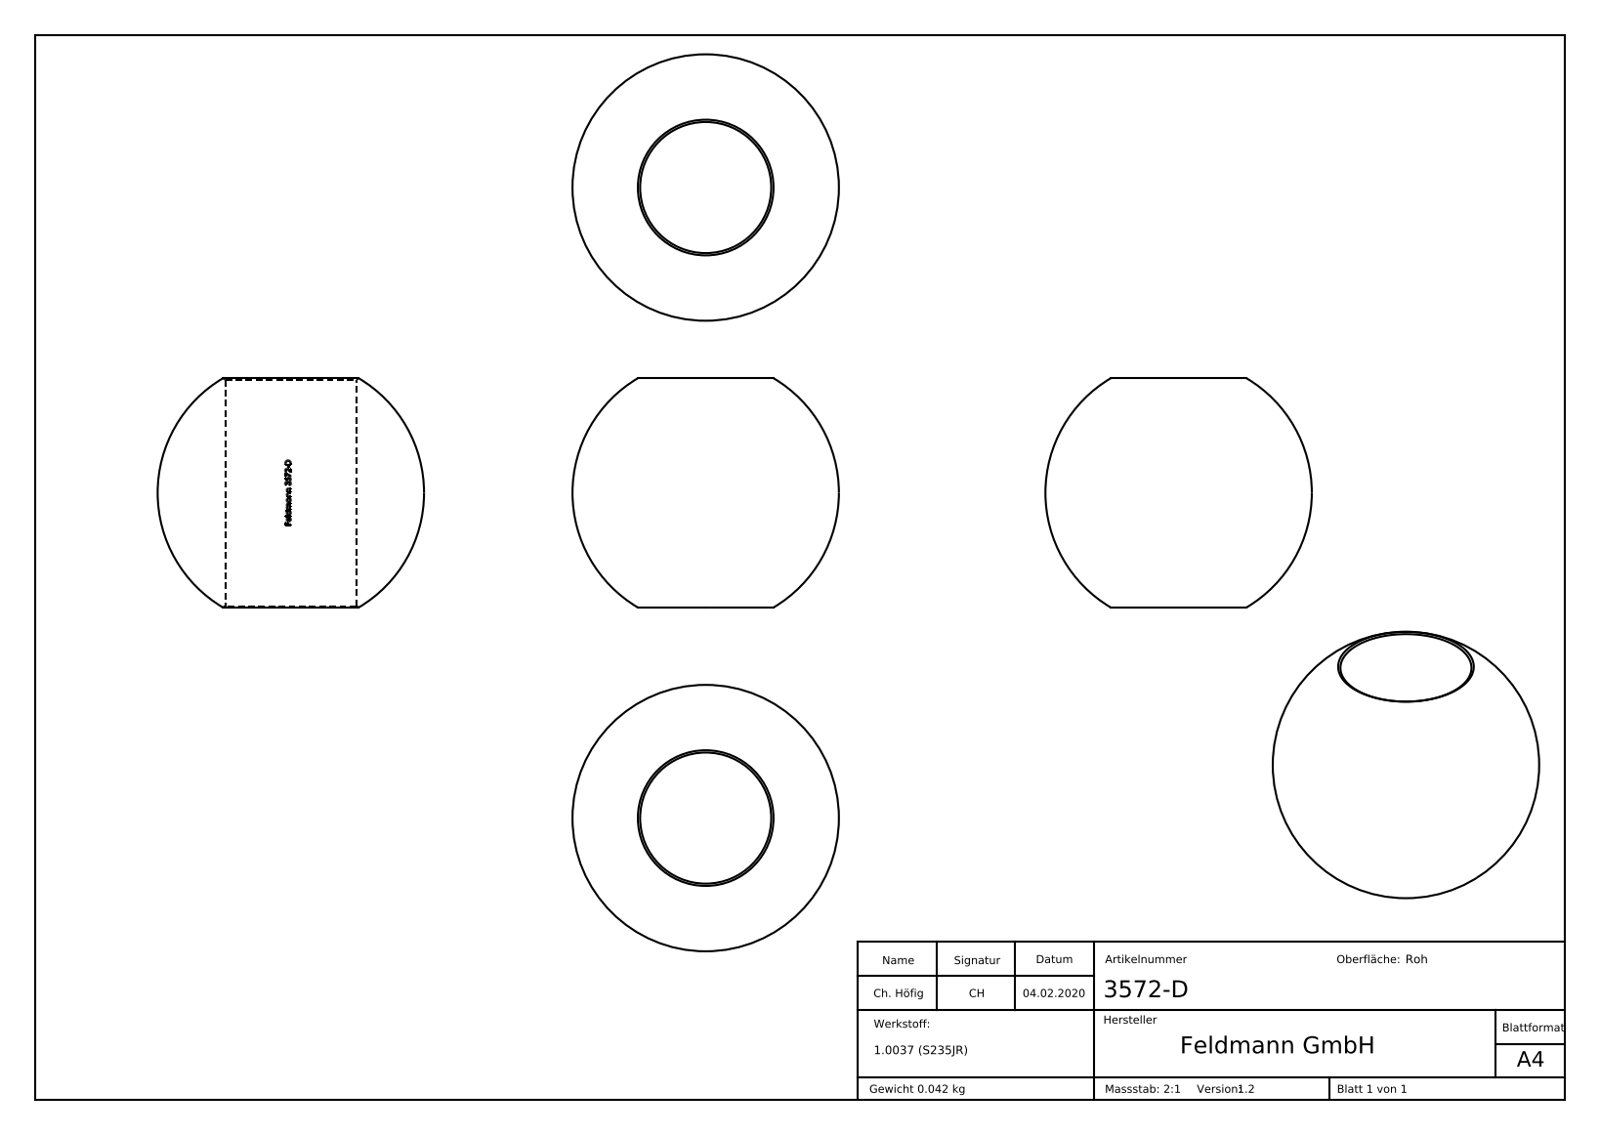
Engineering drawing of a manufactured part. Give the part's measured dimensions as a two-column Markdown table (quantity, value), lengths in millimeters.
| quantity | value |
| --- | --- |
| part name | 3572-D |
| STEP written by | SolidWorks 2015 (CONFIG_CONTROL_DESIGN) |
| units | millimeters |
| bodies | 1 solid, 190 faces (85 planar, 19 cylindrical, 86 other) |
| overall size | 25 × 25 × 21.52 |
| volume | 5 396 mm³ |
| surface area | 2 534 mm² |
| round holes (diameter × count) | 12.3 × 1 |
| partial cylindrical surfaces (radius × count) | 6.25 × 1 |
| main face-to-face distances | 1.19, 0.53, 0.66, 0.45, 3.1, 0.5, 0.8, 1.3, 0.61, 2.65 |
